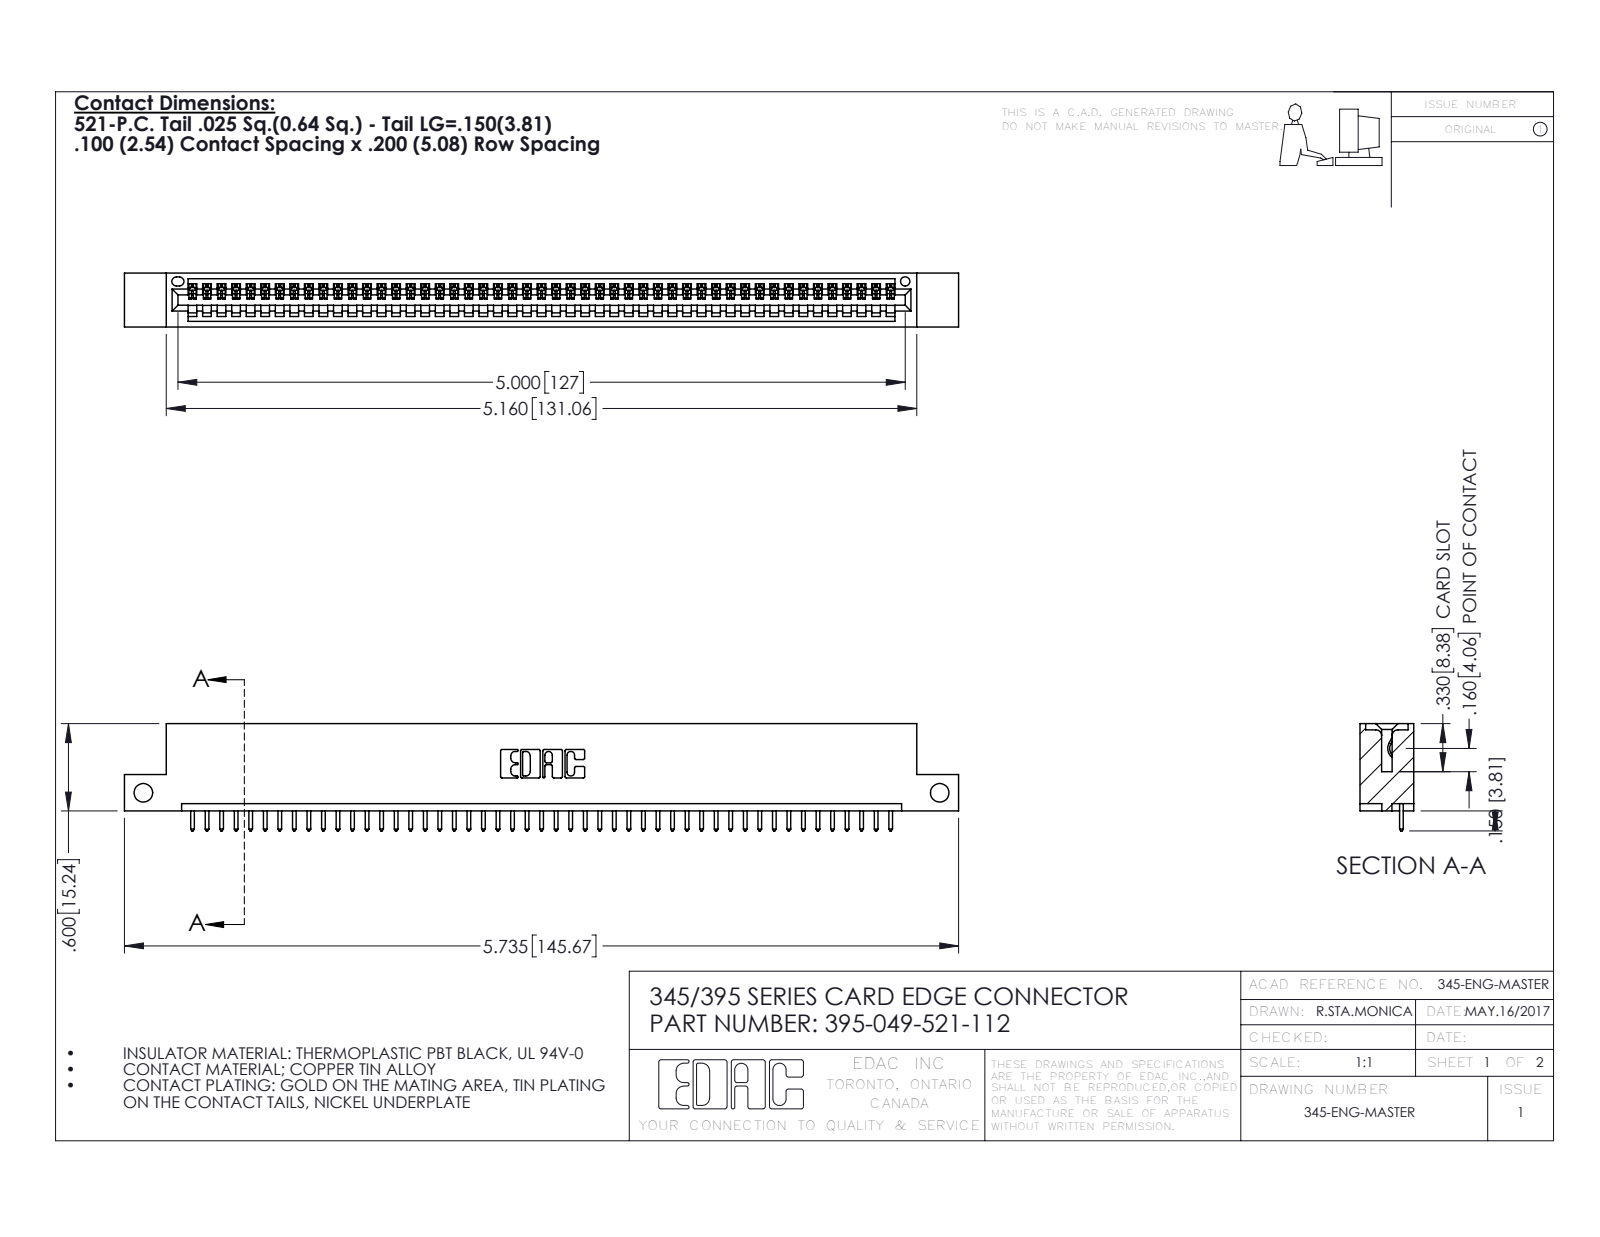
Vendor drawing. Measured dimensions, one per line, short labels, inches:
name: 345-292-001_345-293-121; 345 Part_Flush Mounting Lugs - Side Mount; 395-049-521-112
written by: SolidWorks 2016 (CONFIG_CONTROL_DESIGN)
unit: in
bodies: 50 solids, 2968 faces (2040 planar, 928 cylindrical, 0 other)
size: 5.735 × 0.737 × 0.37
volume: 0.834 in³; area: 27.23 in²
holes: 2× ⌀0.128, 1× ⌀0.064
rounds: 98× R0.006, 98× R0.01, 22× R0.01, 6× R0.007, 6× R0.031, 3× R0.026, 2× R0.031, 2× R0.04
face distances: 0.298, 0.072, 0.37, 0.2, 0.098, 0.272, 0.025, 0.225, 0.149, 0.072
hole spacings: 5.475
